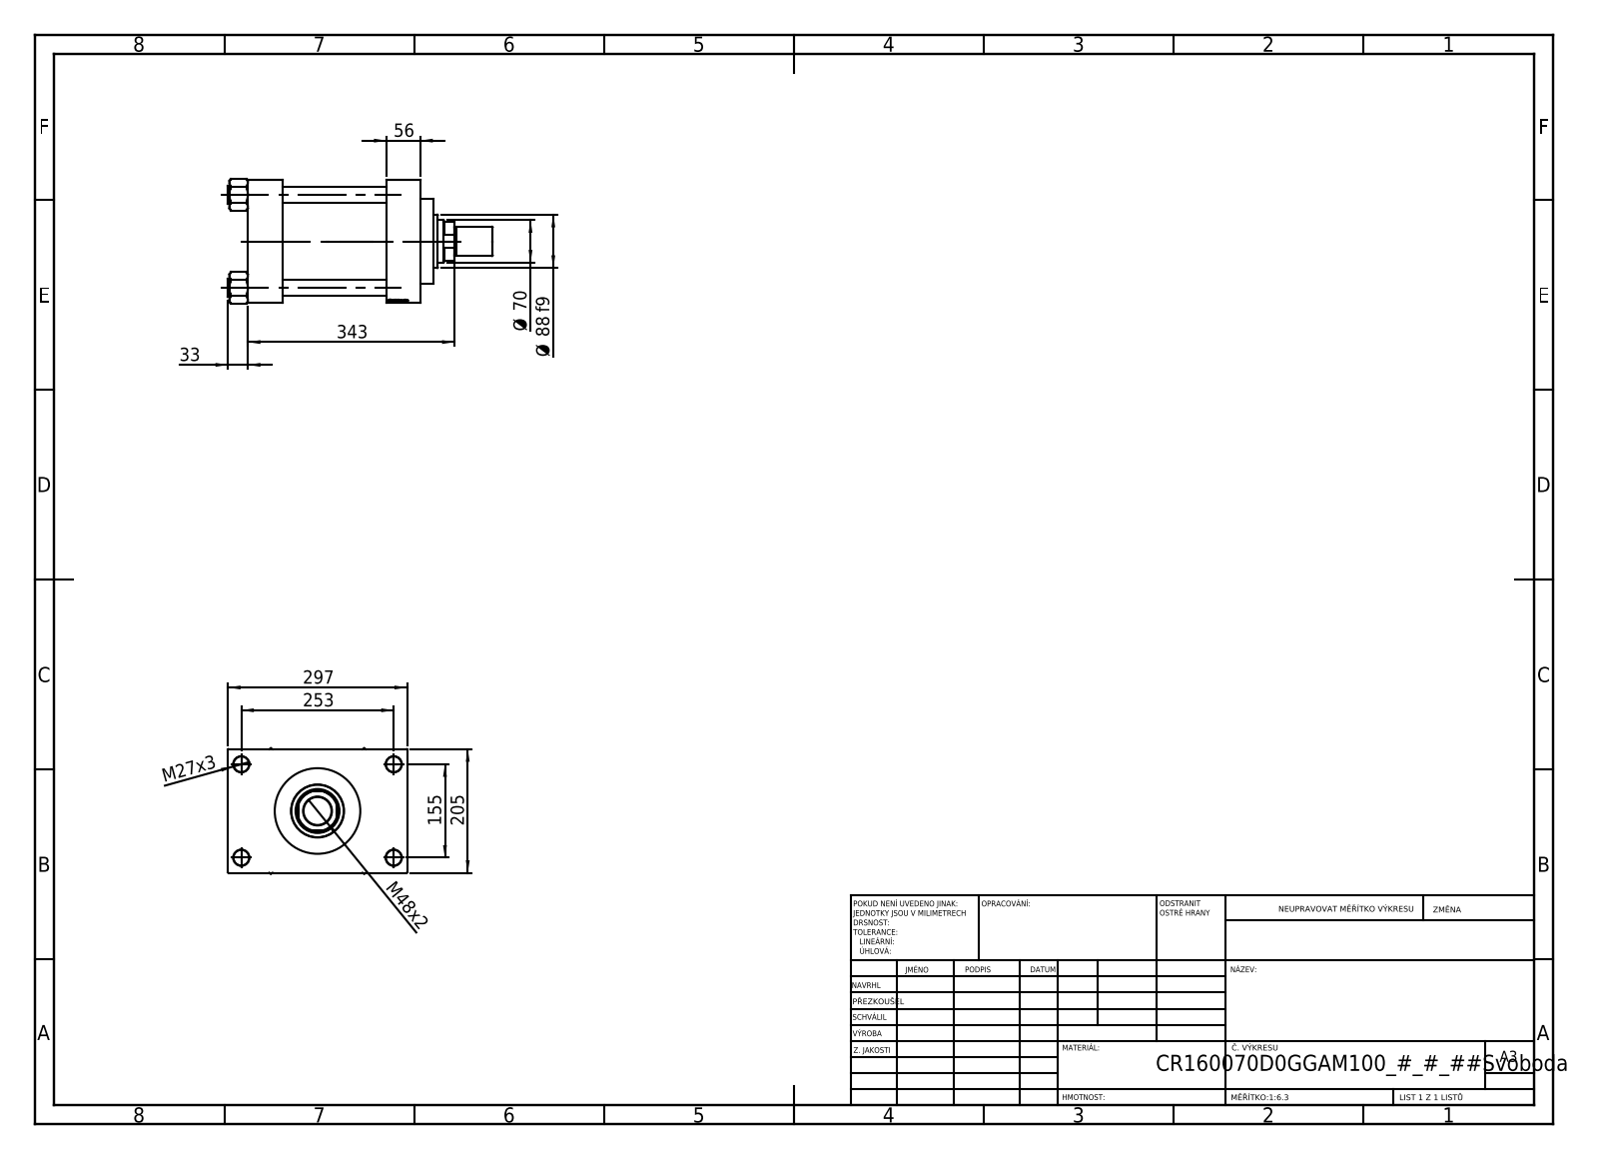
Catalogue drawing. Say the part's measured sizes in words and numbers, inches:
The part is named "NUT_M5_D; V215_VC_A; V215CR_D_TYCINKA; V215CR_D_Body (+2 more)". Its 3-D file was written by "SolidWorks 2019 (CONFIG_CONTROL_DESIGN)". It is 12 solids with 1163 faces: 548 planar, 91 cylindrical and 524 other. Overall it measures 17.283 by 11.693 by 8.194 inches. Its volume is 526.2 cubic inches and its surface area 1 341 square inches. Round holes: 4 of diameter 1.024, 4 of diameter 1.063, 2 of diameter 0.276, 2 of diameter 1.309, 2 of diameter 1.772, 1 of diameter 1.831, 1 of diameter 2.756, 1 of diameter 2.874, 1 of diameter 4.724, 1 of diameter 5.591, 1 of diameter 6.299. Round bosses or shafts: 4 of diameter 1.181, 1 of diameter 6.535, 1 of diameter 3.465, 1 of diameter 1.89, 1 of diameter 1.811. Partial cylindrical surfaces (rounded edges, fillets, slot ends): 1 of radius 1.339. The main face-to-face distances are 2.283, 9.055, 6.772, 11.26, 8.976, 2.205, 8.071, 1.811, 9.882, 3.937. The hole center spacings are 1.931, 4.312, 5.841, 6.098, 6.399, 8.03, 10.084, 6.102.
